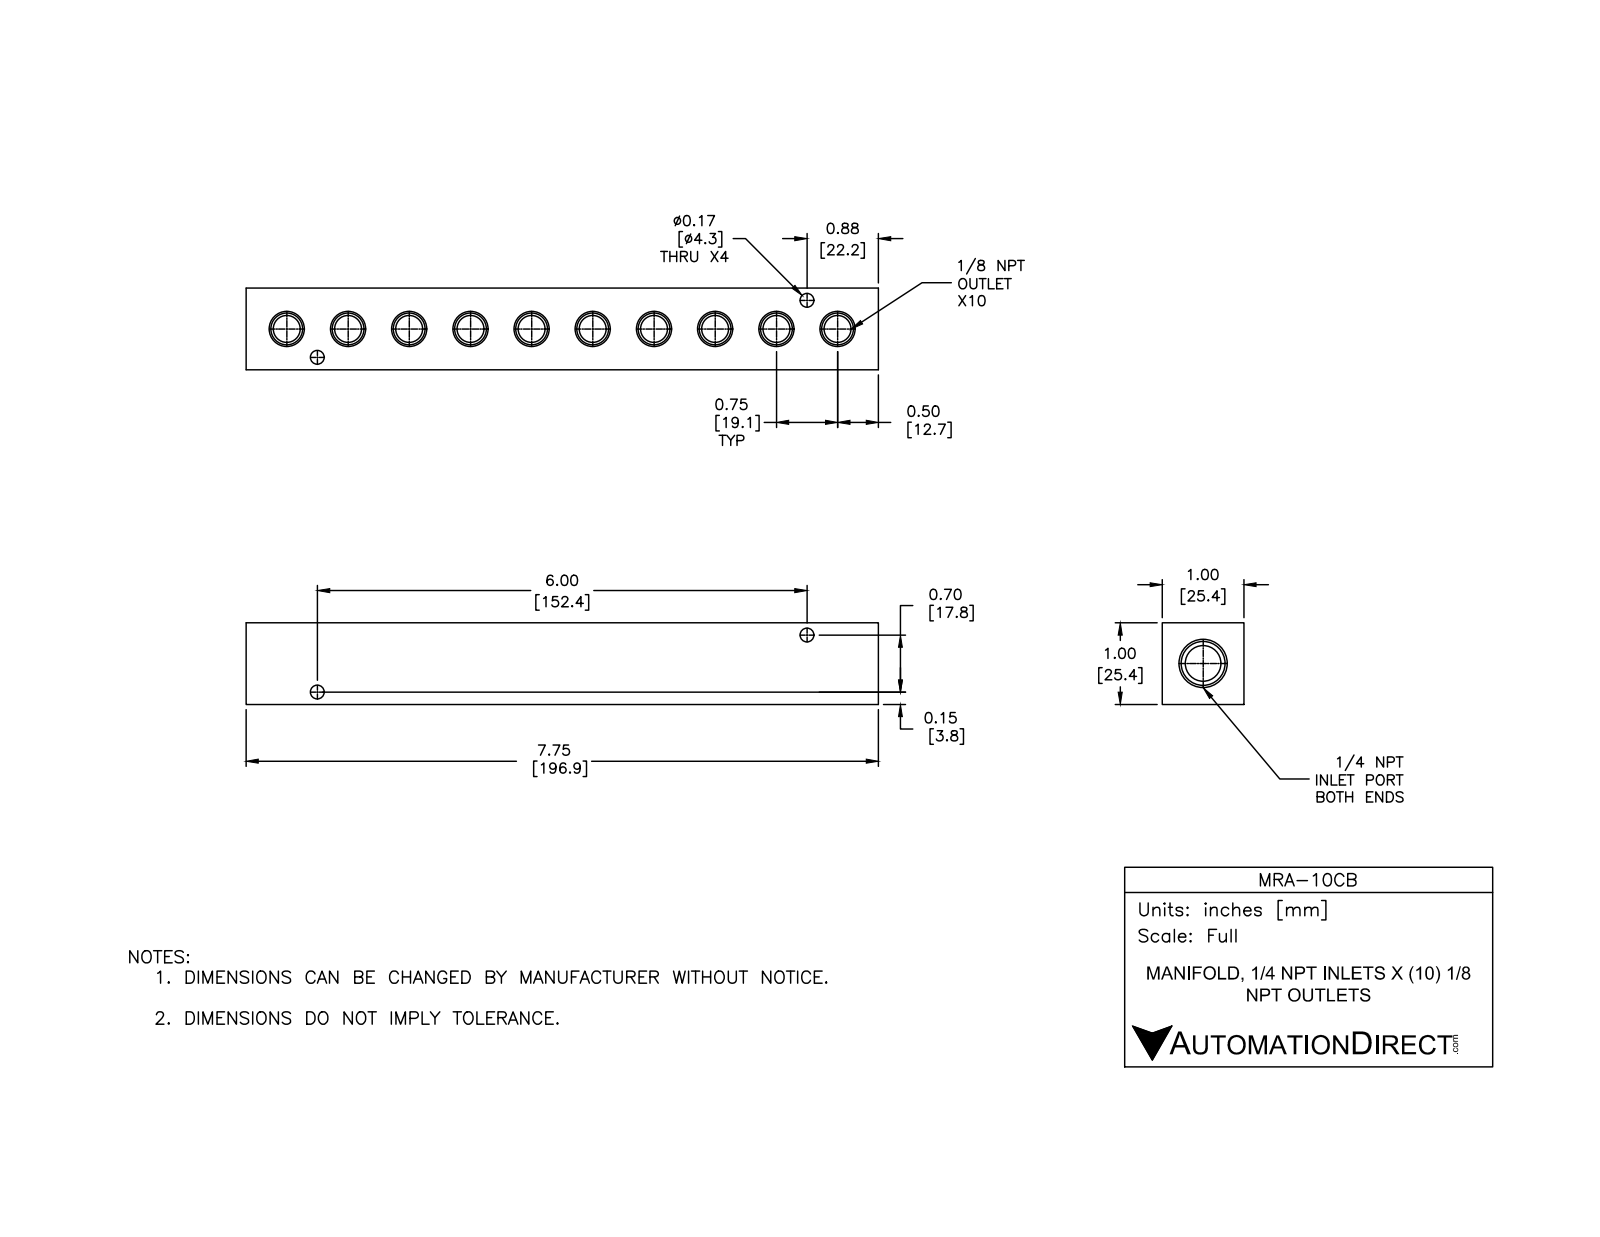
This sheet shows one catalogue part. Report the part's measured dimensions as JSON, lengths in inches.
{"part_name": "MRA-10CB", "step_written_by": "SolidWorks 2015 (CONFIG_CONTROL_DESIGN)", "units": "inches", "bodies": {"solids": 1, "faces": 103, "planar": 18, "cylindrical": 37, "other": 48}, "overall_size": [7.75, 1, 1], "volume_in3": 6.083, "surface_area_in2": 47.01, "round_holes": [[0.332, 8], [0.17, 4], [0.438, 1]], "partial_cylinders_radius": [[0.166, 2]], "face_to_face_distances": [1, 7.75, 0.73, 0.27, 0.39, 7.36, 6.97], "hole_center_spacings": [0.75, 1.5, 2.25, 3, 0.513, 1.178, 3.75, 4.887]}
